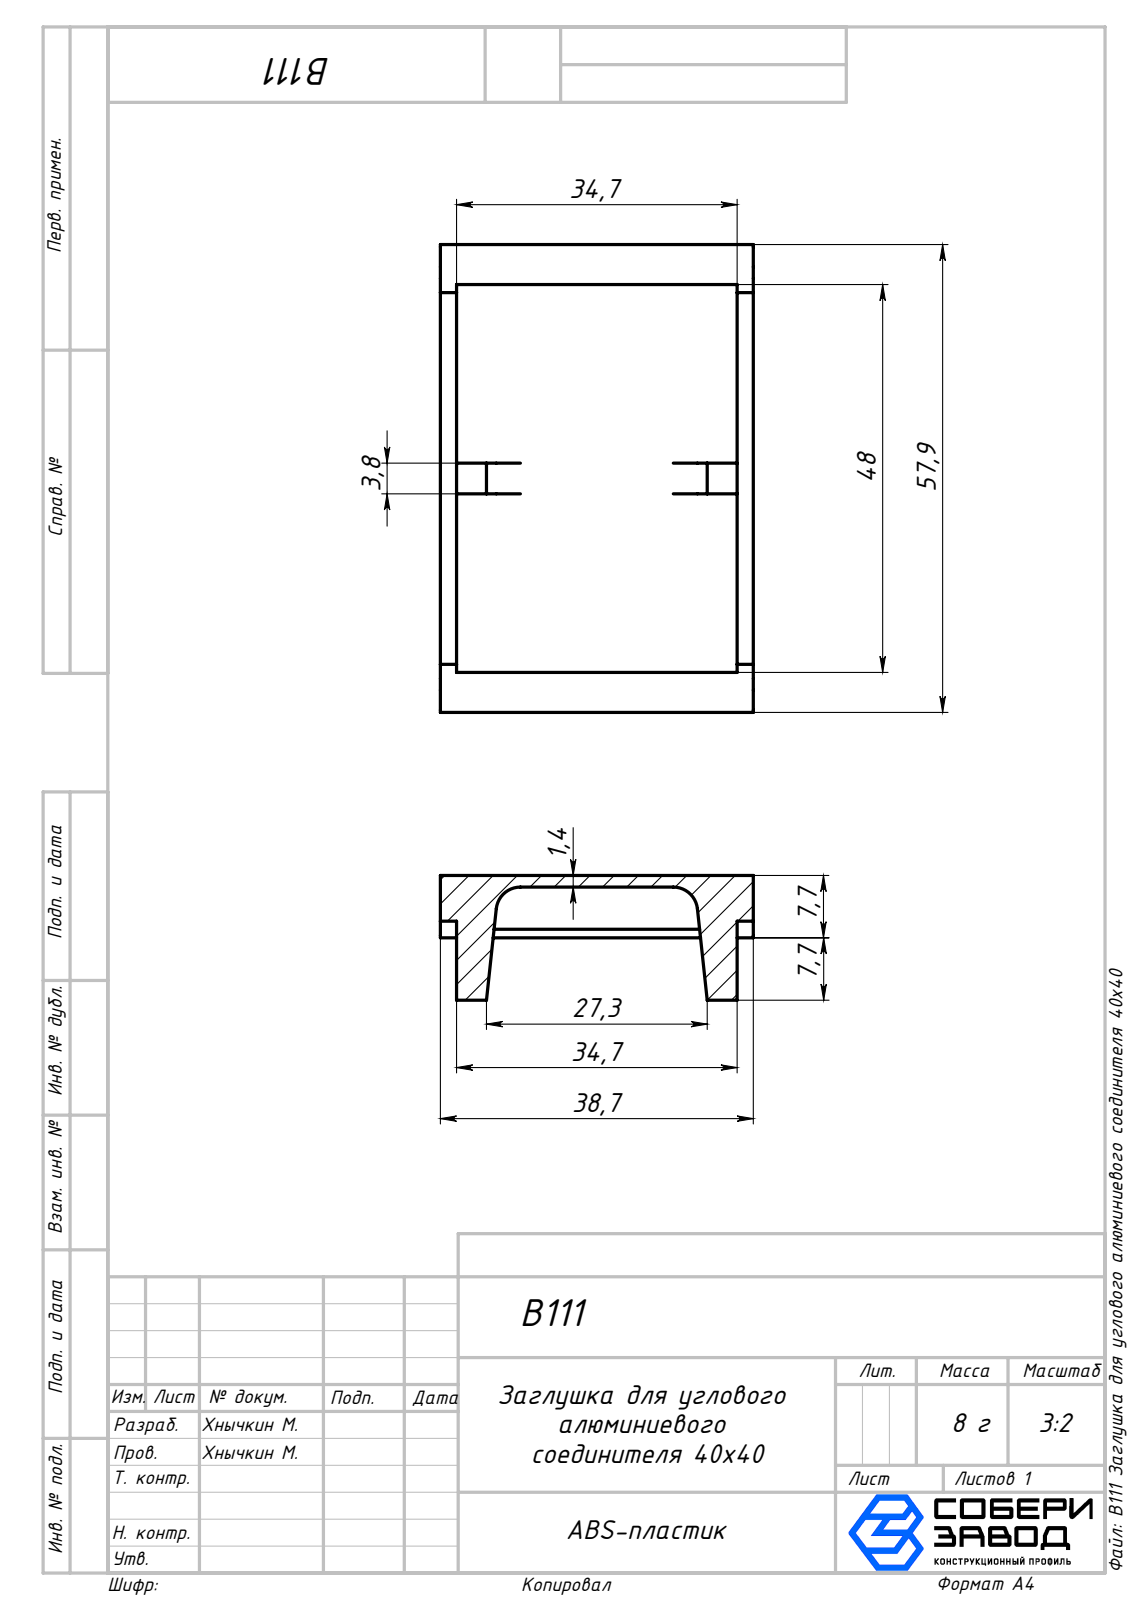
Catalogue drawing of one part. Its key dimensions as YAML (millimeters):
part_name: "B111 Заглушка для углового алюминиевого соединителя 40х40"
step_written_by: "SolidWorks 2025 (AUTOMOTIVE_DESIGN)"
units: millimeters
bodies: {solids: 1, faces: 37, planar: 28, cylindrical: 9, other: 0}
overall_size: [57.9, 38.7, 15.44]
volume: 5943
surface_area: 6589
partial_cylinders:
  - {radius: 1, count: 6}
  - {radius: 3, count: 2}
face_to_face_distances: [1.44, 2, 36.7, 38.7, 41.52, 22.1, 25.9, 34.7, 4.22, 5.66]
